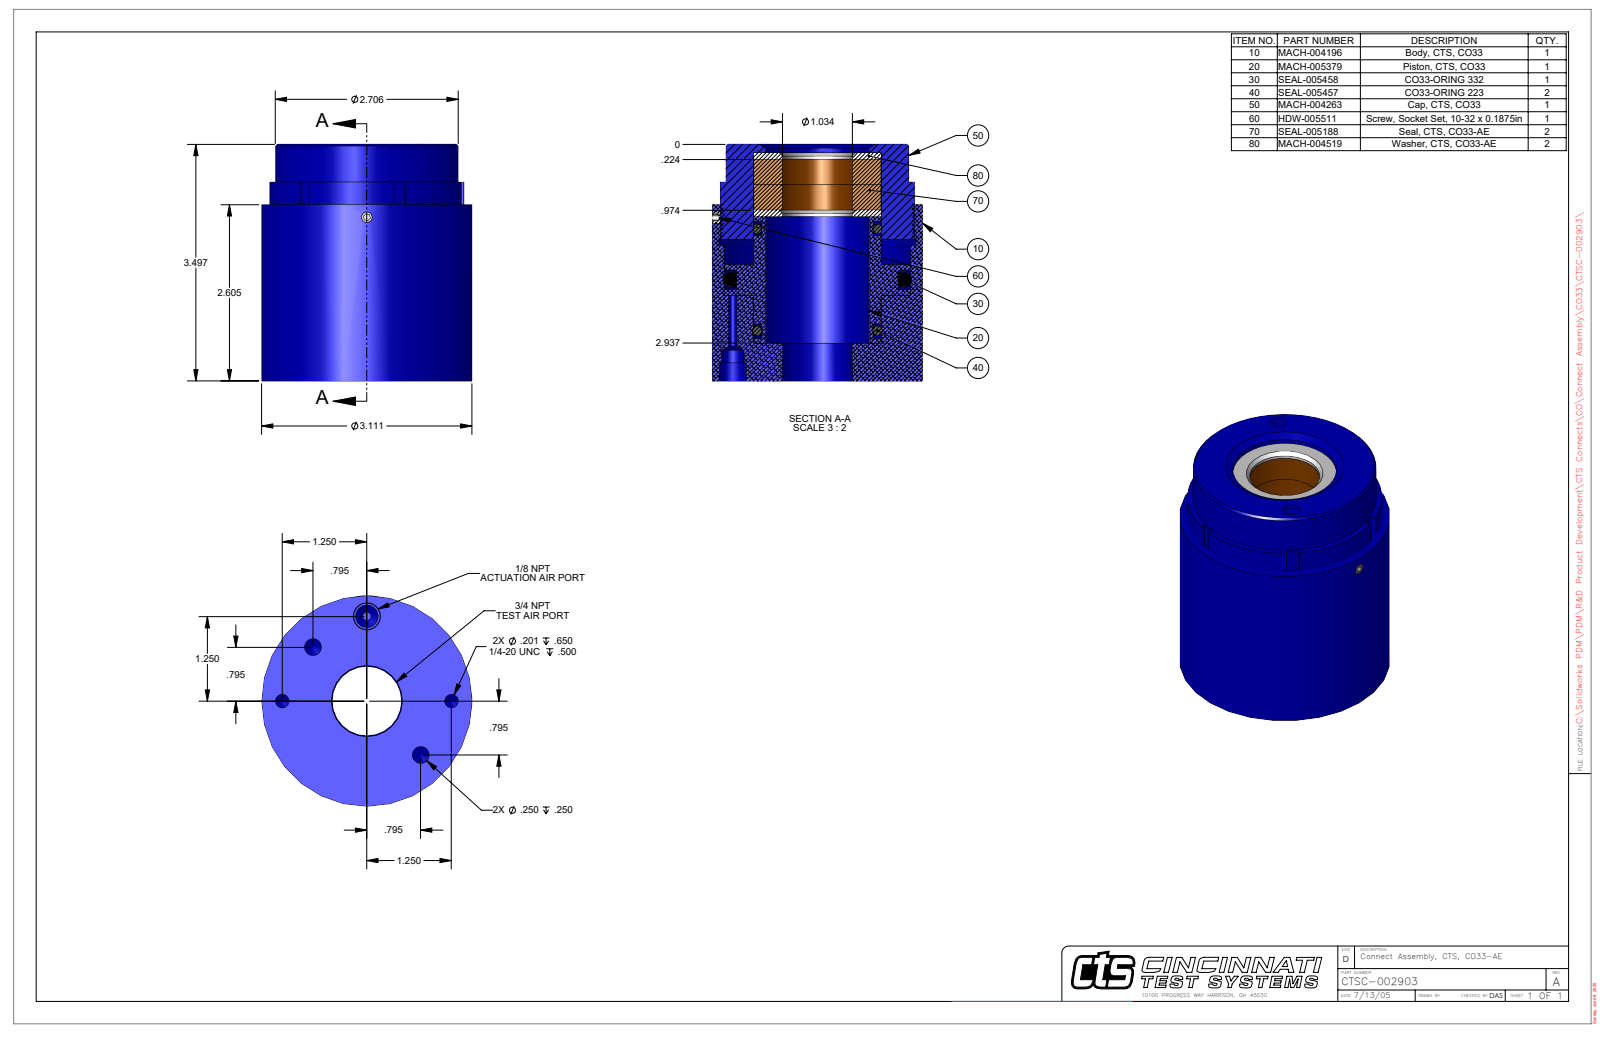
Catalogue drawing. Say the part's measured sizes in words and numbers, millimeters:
The part is named "CTSC-002903". Its 3-D file was written by "SolidWorks 2023 (AUTOMOTIVE_DESIGN)". It is 1 solid with 122 faces: 49 planar, 53 cylindrical and 20 other. Overall it measures 88.8 by 79 by 79 millimeters. Its volume is 328 700 cubic millimeters and its surface area 42 720 square millimeters. Round holes: 4 of diameter 6.4, 2 of diameter 5.1, 1 of diameter 2.4, 1 of diameter 3.2, 1 of diameter 4, 1 of diameter 8.4, 1 of diameter 26.3, 1 of diameter 26.3, 1 of diameter 38.8, 1 of diameter 38.8, 1 of diameter 48.1. Round bosses or shafts: 1 of diameter 79, 1 of diameter 73, 1 of diameter 68.7, 1 of diameter 47.9. Partial cylindrical surfaces (rounded edges, fillets, slot ends): 1 of radius 35.7, 1 of radius 39.1. The main face-to-face distances are 88.8, 14.2, 74.6, 66.2, 22.7, 51.9, 61.7, 47.5, 4.5, 27.1. The hole center spacings are 28.6, 23.3, 31.8, 55.8, 2.4, 25.6, 44.9, 54.7.
